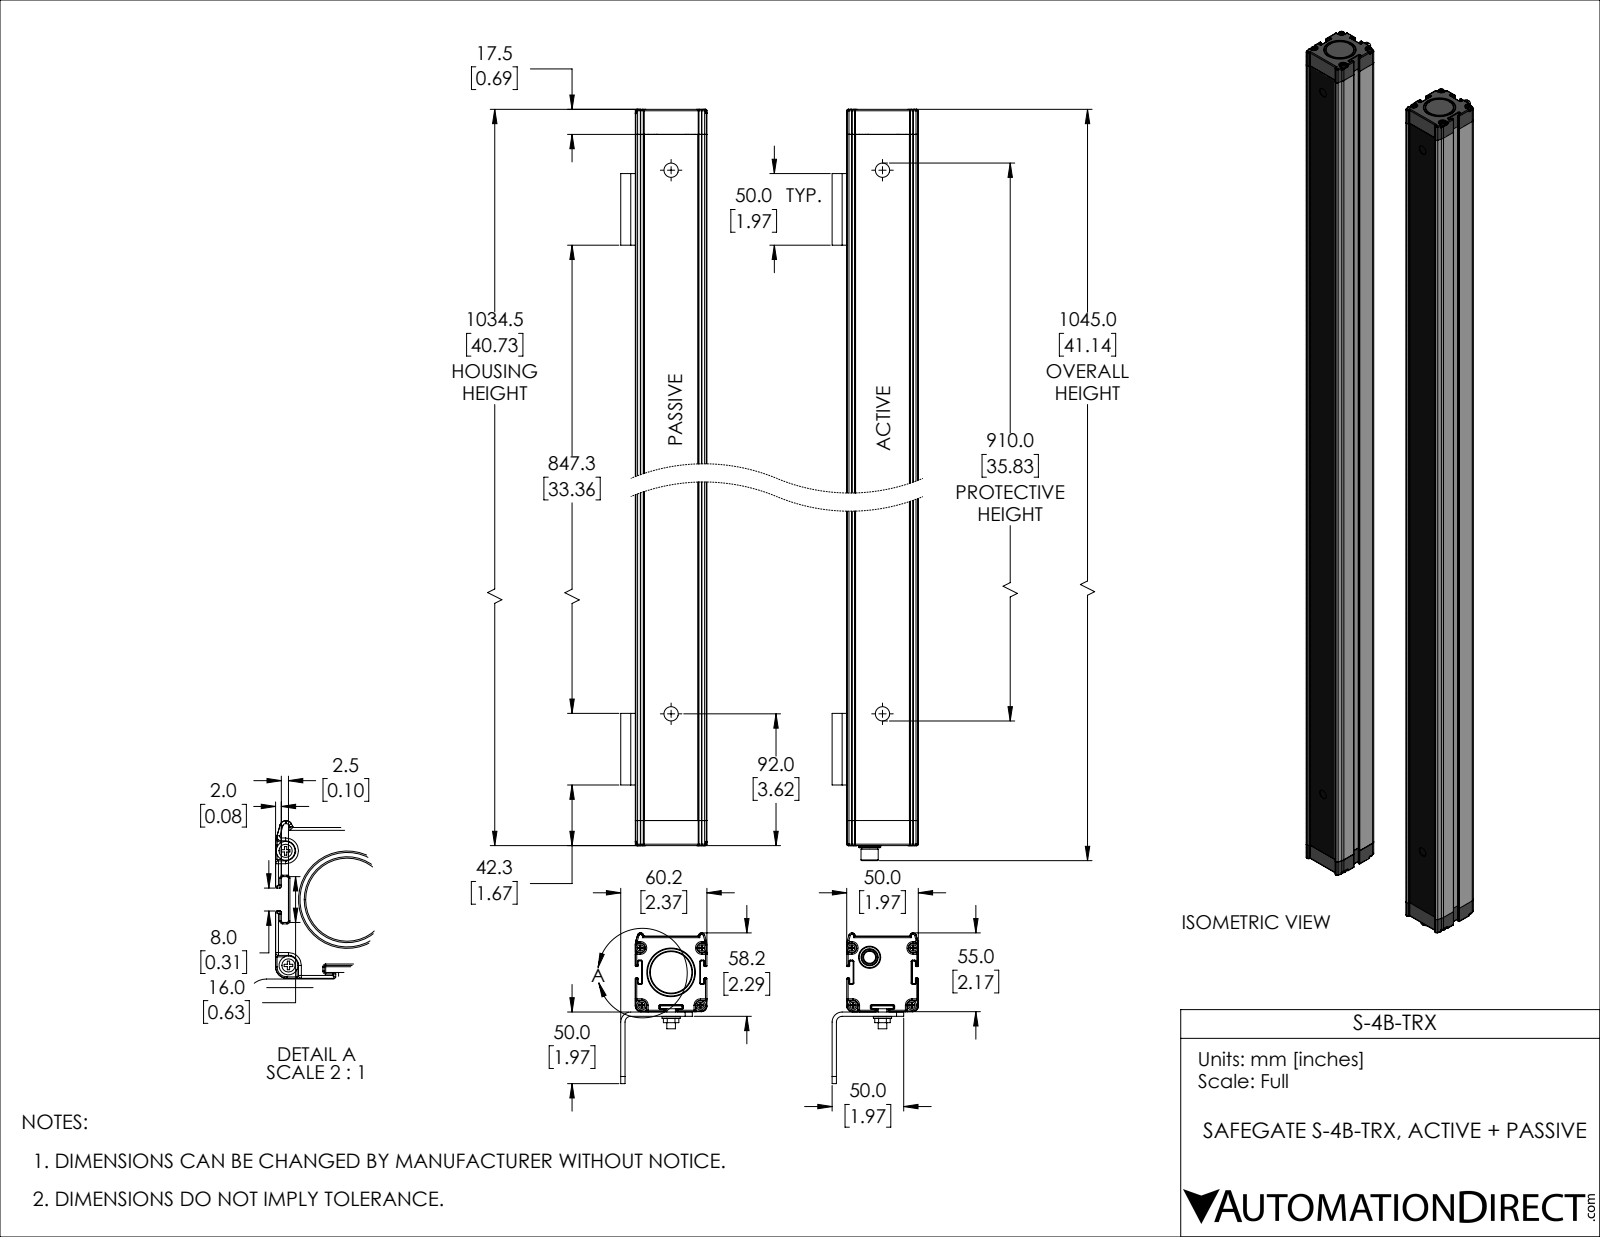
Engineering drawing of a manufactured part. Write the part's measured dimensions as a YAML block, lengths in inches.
part_name: "S-4B-TRX_2; S-4B-TRX; S-4B-TRX_1"
step_written_by: "SolidWorks 2019 (AUTOMOTIVE_DESIGN)"
units: inches
bodies: {solids: 49, faces: 4107, planar: 1848, cylindrical: 1533, other: 726}
overall_size: [41.146, 9.11, 4.733]
volume: 105.6
surface_area: 2071
round_holes:
  - {diameter: 0.138, count: 8}
  - {diameter: 0.236, count: 8}
  - {diameter: 0.31, count: 8}
  - {diameter: 0.394, count: 5}
  - {diameter: 0.472, count: 3}
  - {diameter: 0.551, count: 3}
  - {diameter: 0.079, count: 2}
  - {diameter: 0.378, count: 1}
round_bosses_or_shafts:
  - {diameter: 0.177, count: 10}
  - {diameter: 0.5, count: 8}
  - {diameter: 0.26, count: 8}
  - {diameter: 0.591, count: 4}
  - {diameter: 0.61, count: 1}
  - {diameter: 0.472, count: 1}
  - {diameter: 0.433, count: 1}
partial_cylinders:
  - {radius: 0.02, count: 431}
  - {radius: 0.039, count: 212}
  - {radius: 0.012, count: 53}
  - {radius: 0.128, count: 32}
  - {radius: 0.138, count: 16}
  - {radius: 0.197, count: 16}
  - {radius: 0.059, count: 13}
  - {radius: 0.079, count: 9}
face_to_face_distances: [0.59, 0.098, 6.74, 0.177, 0.276, 1.693, 1.791, 0.079, 0.118, 1.969]
hole_center_spacings: [6.74, 0.406, 1.139, 1.181, 1.575, 2.283, 6.765, 6.843]
